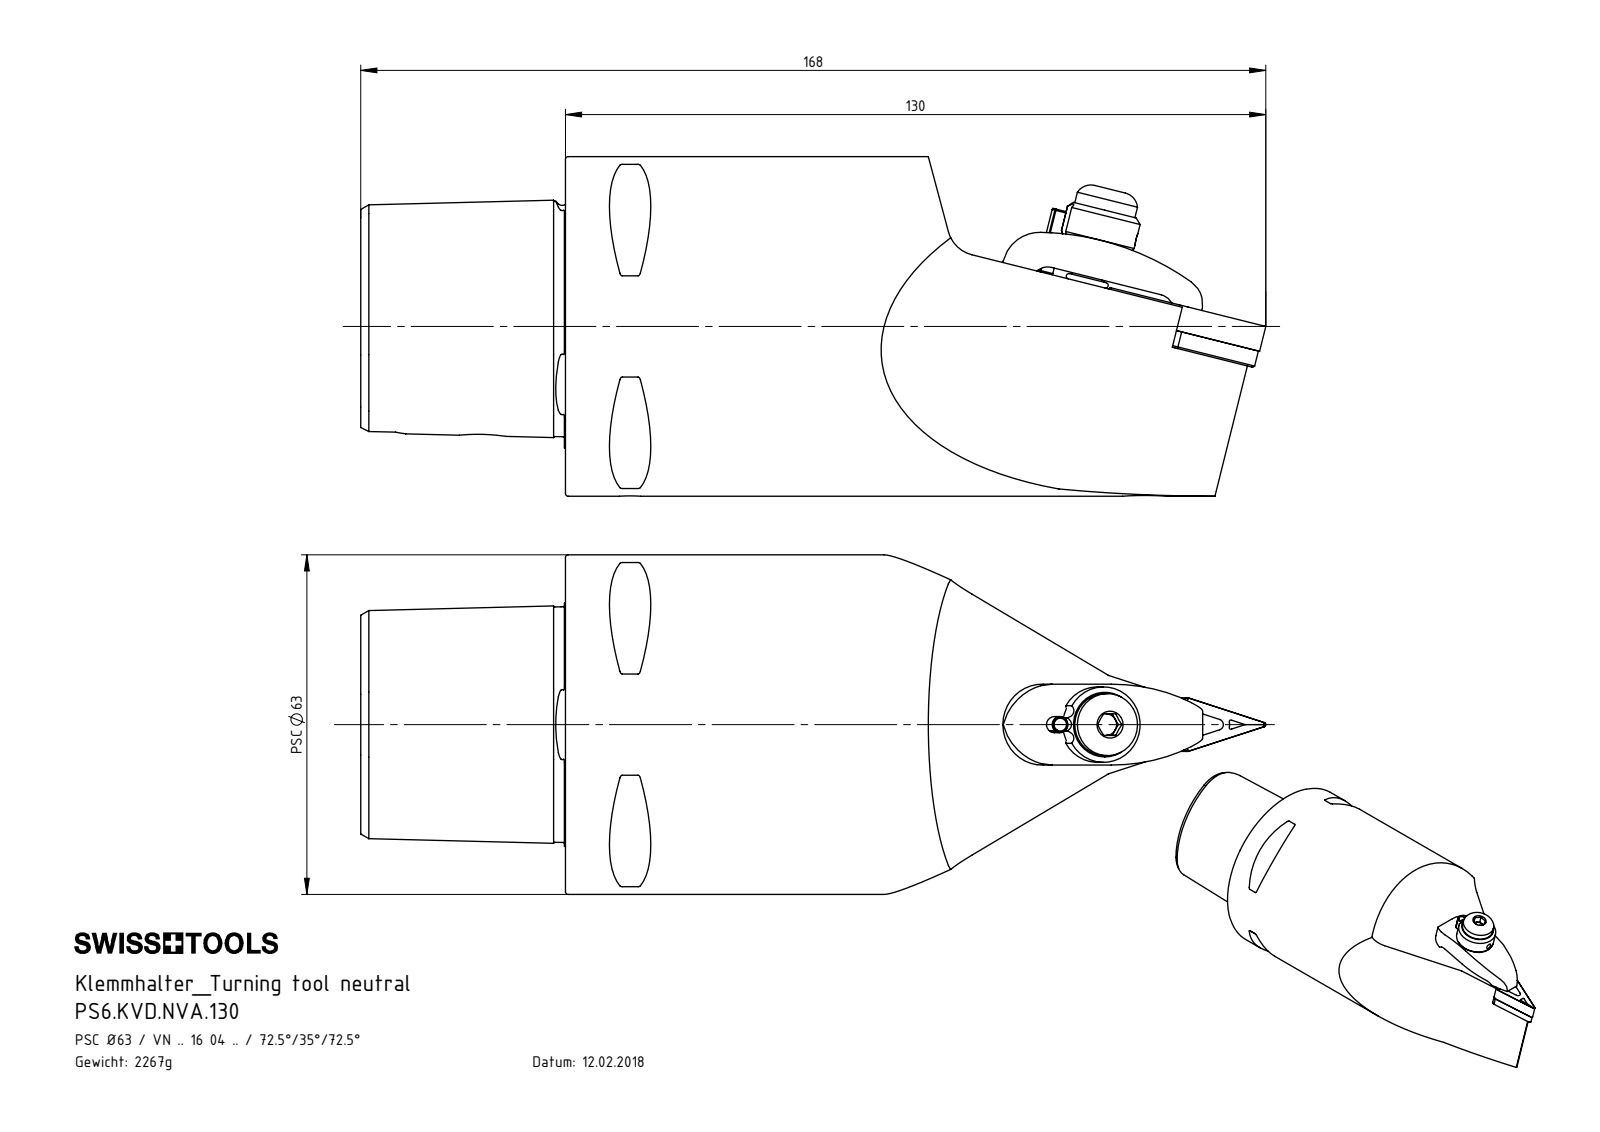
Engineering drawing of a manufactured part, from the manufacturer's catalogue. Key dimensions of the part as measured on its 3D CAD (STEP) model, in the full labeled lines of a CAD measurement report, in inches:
Part name (STEP PRODUCT): PS6-KVD.NVA.130; KVT_MB_600_060; ISO 13337 - 3 x 12_PreviewCfg; WCC-ER4.103.032_A (+7 more)
STEP written by: SolidWorks 2012 (CONFIG_CONTROL_DESIGN)
Units: inches
Bodies: 11 solids, 425 faces (99 planar, 132 cylindrical, 194 other)
Overall size (bounding box): 6.614 × 2.48 × 2.48
Volume: 17.59 in³ · Surface area: 65.92 in²
Round holes (diameter × count): ⌀0.079 ×3, ⌀0.197 ×3, ⌀0.276 ×2, ⌀0.335 ×2, ⌀0.094 ×1, ⌀0.118 ×1, ⌀0.13 ×1, ⌀0.15 ×1, ⌀0.157 ×1, ⌀0.195 ×1, ⌀0.236 ×1, ⌀0.244 ×1
Round bosses / shafts (diameter × count): ⌀0.236 ×2, ⌀0.118 ×2, ⌀2.48 ×1, ⌀0.551 ×1, ⌀0.453 ×1, ⌀0.276 ×1, ⌀0.268 ×1, ⌀0.244 ×1
Partial cylindrical surfaces — rounded edges, fillets, slot ends (radius × count): R0.02 ×10, R0.015 ×6, R0.027 ×6, R0.016 ×4, R0.059 ×3, R0.079 ×2, R0.118 ×2, R0.236 ×2
Main face-to-face distances: 0.352, 1.496, 0.98, 0.176, 0.227, 0.051, 0.125, 0.301, 1.063, 0.433
Hole centre spacings: 0.316, 0.316, 0.322, 0.323, 0.753, 0.759, 0.76, 1.075
